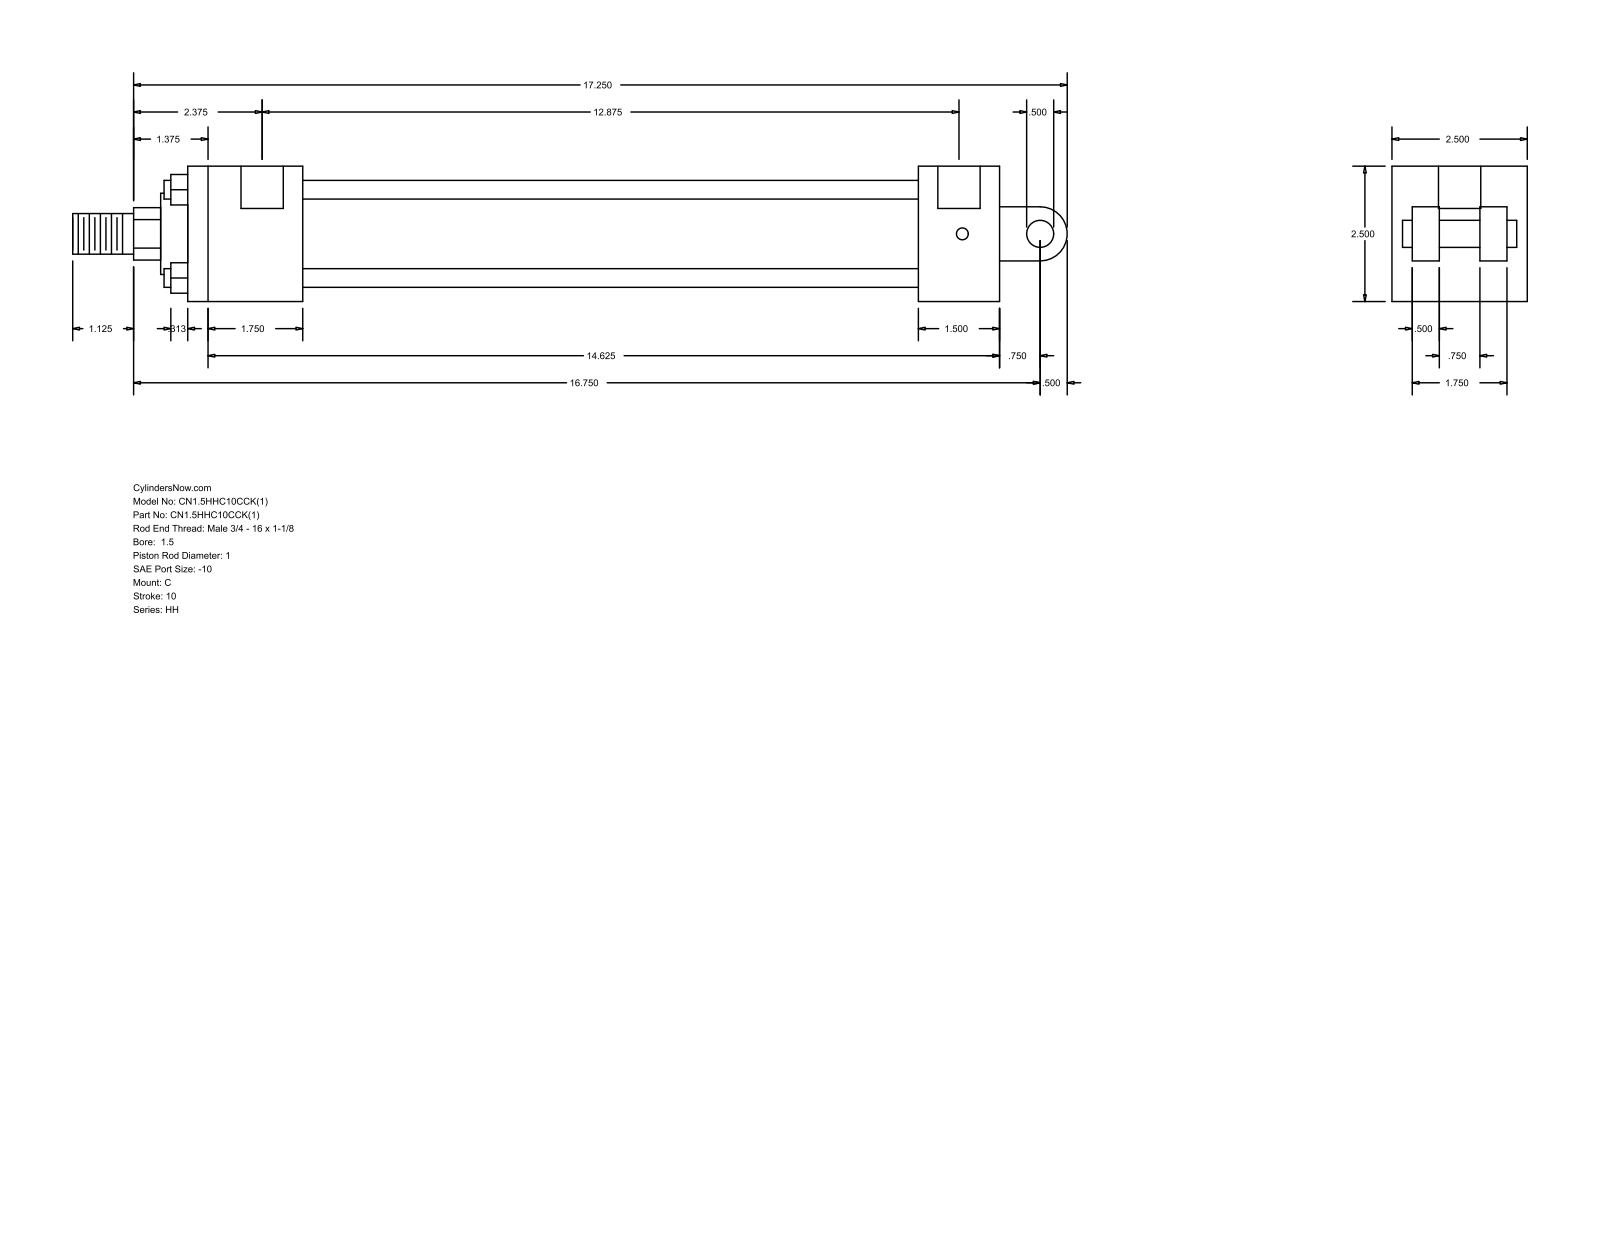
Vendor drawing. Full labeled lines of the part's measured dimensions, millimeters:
Part name (STEP PRODUCT): HH_C__0150_1
STEP written by: GSSL Pune (CONFIG_CONTROL_DESIGN)
Units: millimetres
Bodies: 0 solids, 99 faces (70 planar, 29 cylindrical, 0 other)
Overall size (bounding box): 466.73 × 63.5 × 63.5
Round holes (diameter × count): ⌀5.56 ×4, ⌀19.84 ×2
Round bosses / shafts (diameter × count): ⌀8.76 ×4, ⌀44.45 ×1, ⌀38.1 ×1, ⌀25.4 ×1, ⌀19.05 ×1, ⌀12.7 ×1
Partial cylindrical surfaces — rounded edges, fillets, slot ends (radius × count): R12.29 ×1, R12.7 ×1
Main face-to-face distances: 63.5, 53.98, 38.1, 288.92, 327.02, 342.9, 381, 12.7, 22.22, 41.28
Hole centre spacings: 1.59, 328.61, 330.2, 327.02
